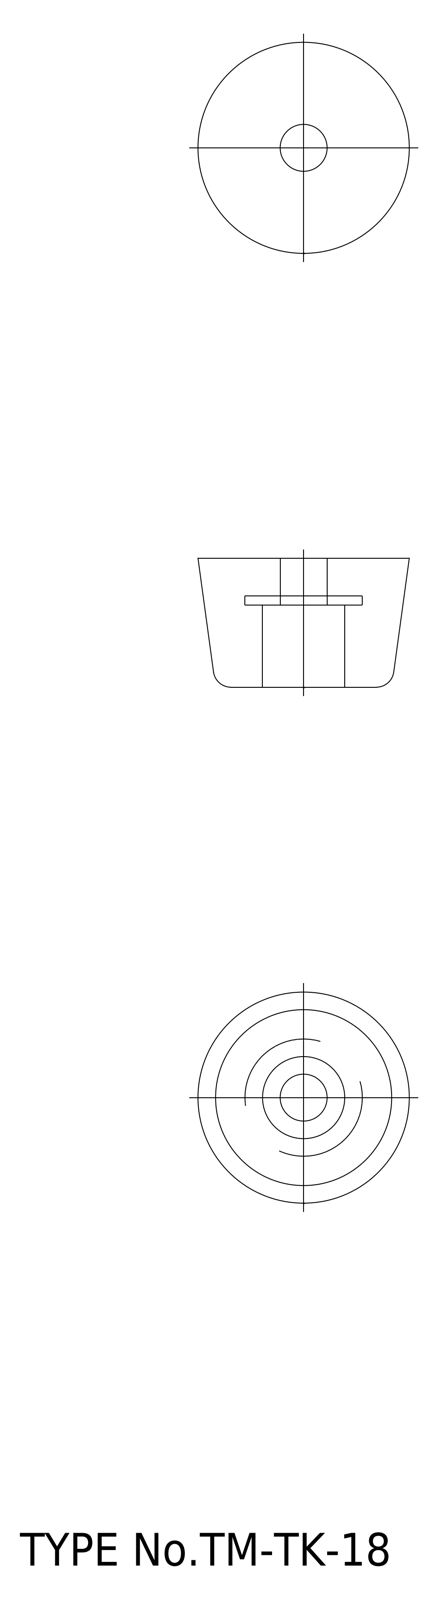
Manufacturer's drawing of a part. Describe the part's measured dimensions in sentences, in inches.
The part is named "washer; rubber foot; TK_18_9258_36". Its 3-D file was written by "CADfix (AUTOMOTIVE_DESIGN)". It is 2 solids with 20 faces: 0 planar, 0 cylindrical and 20 other. Overall it measures 0.709 by 0.709 by 0.433 inches. Its volume is 0.124 cubic inches and its surface area 2.21 square inches.
